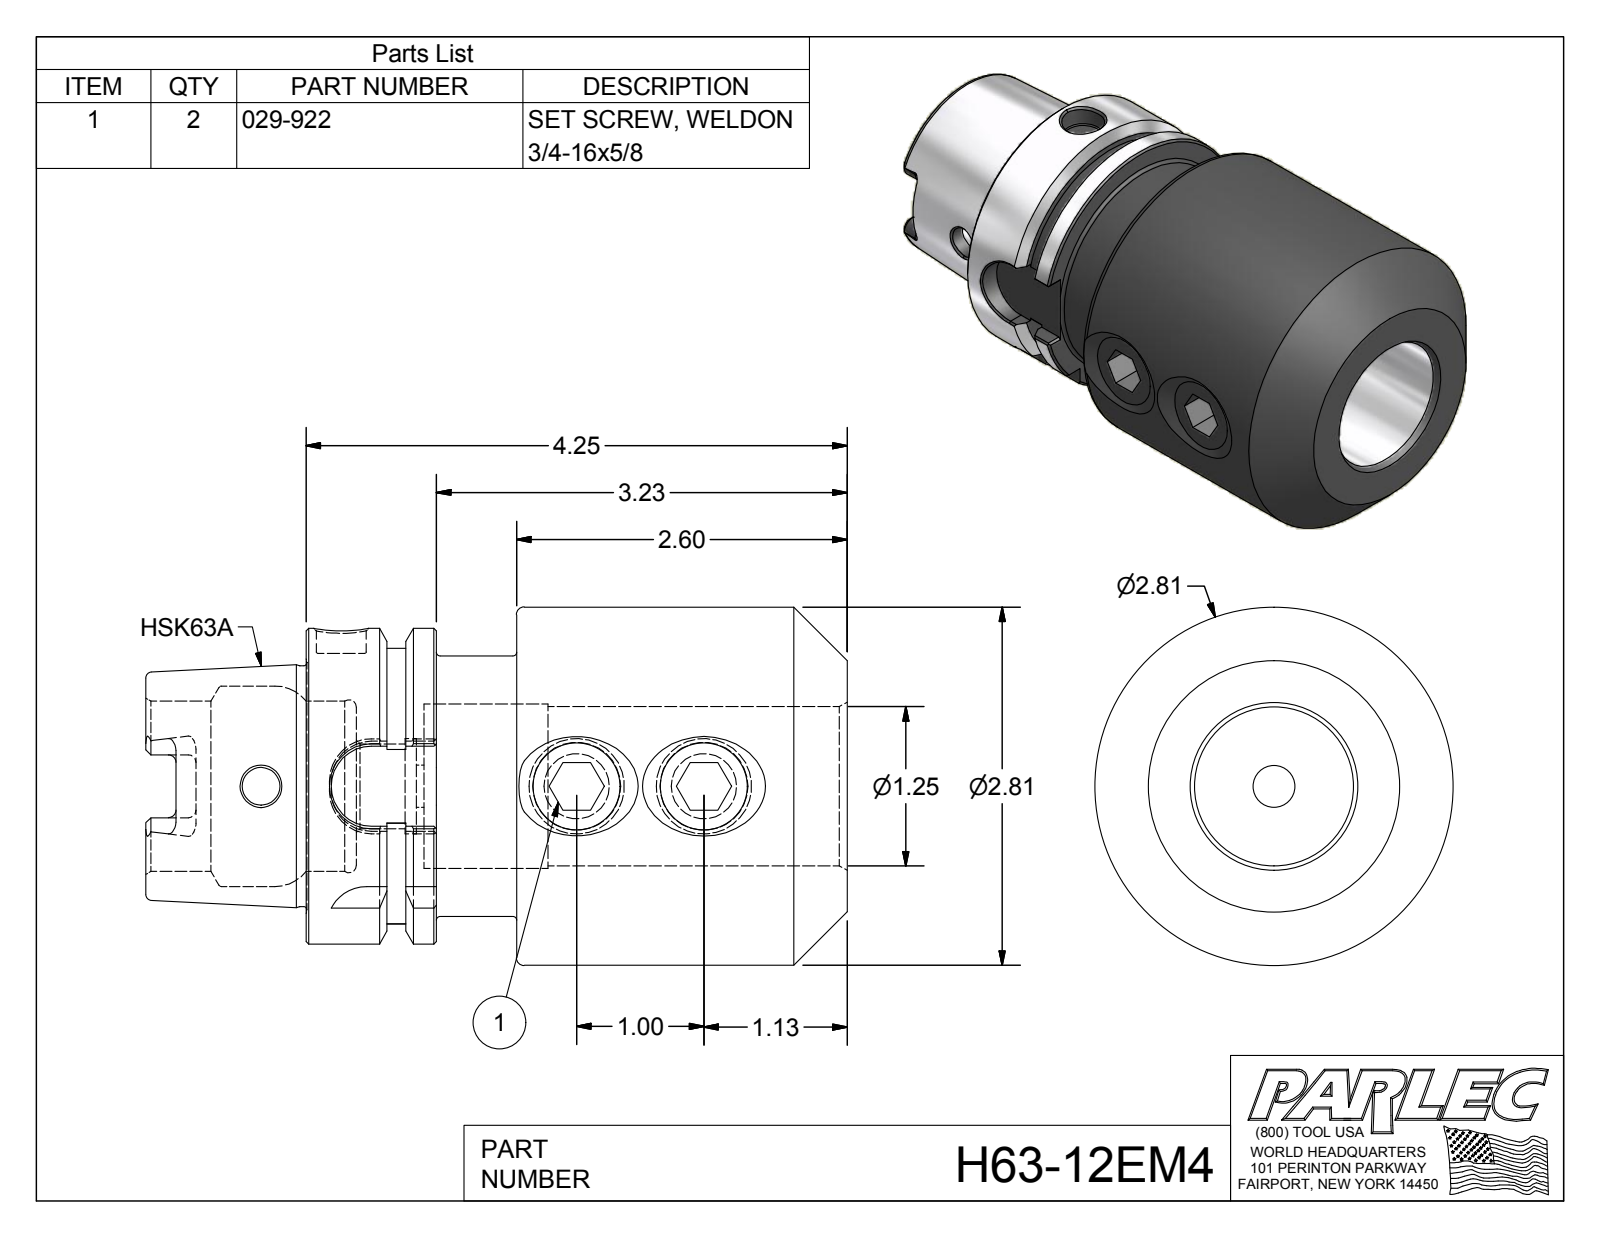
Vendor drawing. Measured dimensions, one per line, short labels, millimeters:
name: H63-12EM4; H63-12EM4-1; 029-922
written by: Autodesk Inventor 2012 (AUTOMOTIVE_DESIGN)
unit: mm
bodies: 3 solids, 173 faces (77 planar, 41 cylindrical, 55 other)
size: 140 × 71.5 × 71.5
volume: 297 300 mm³; area: 54 840 mm²
holes: 2× ⌀17.3, 1× ⌀7.5, 1× ⌀8.4, 1× ⌀10, 1× ⌀16.9, 1× ⌀19, 1× ⌀31.8, 1× ⌀32.8, 1× ⌀34, 1× ⌀40
bosses: 2× ⌀19.1, 1× ⌀71.5, 1× ⌀63, 1× ⌀52, 1× ⌀48
rounds: 6× R1.5, 4× R2.9, 4× R8, 1× R27.5
face distances: 42, 16, 65.9, 108, 32, 23.5, 18.5, 84.4, 26, 6.1
hole spacings: 25.4, 63, 88.4
